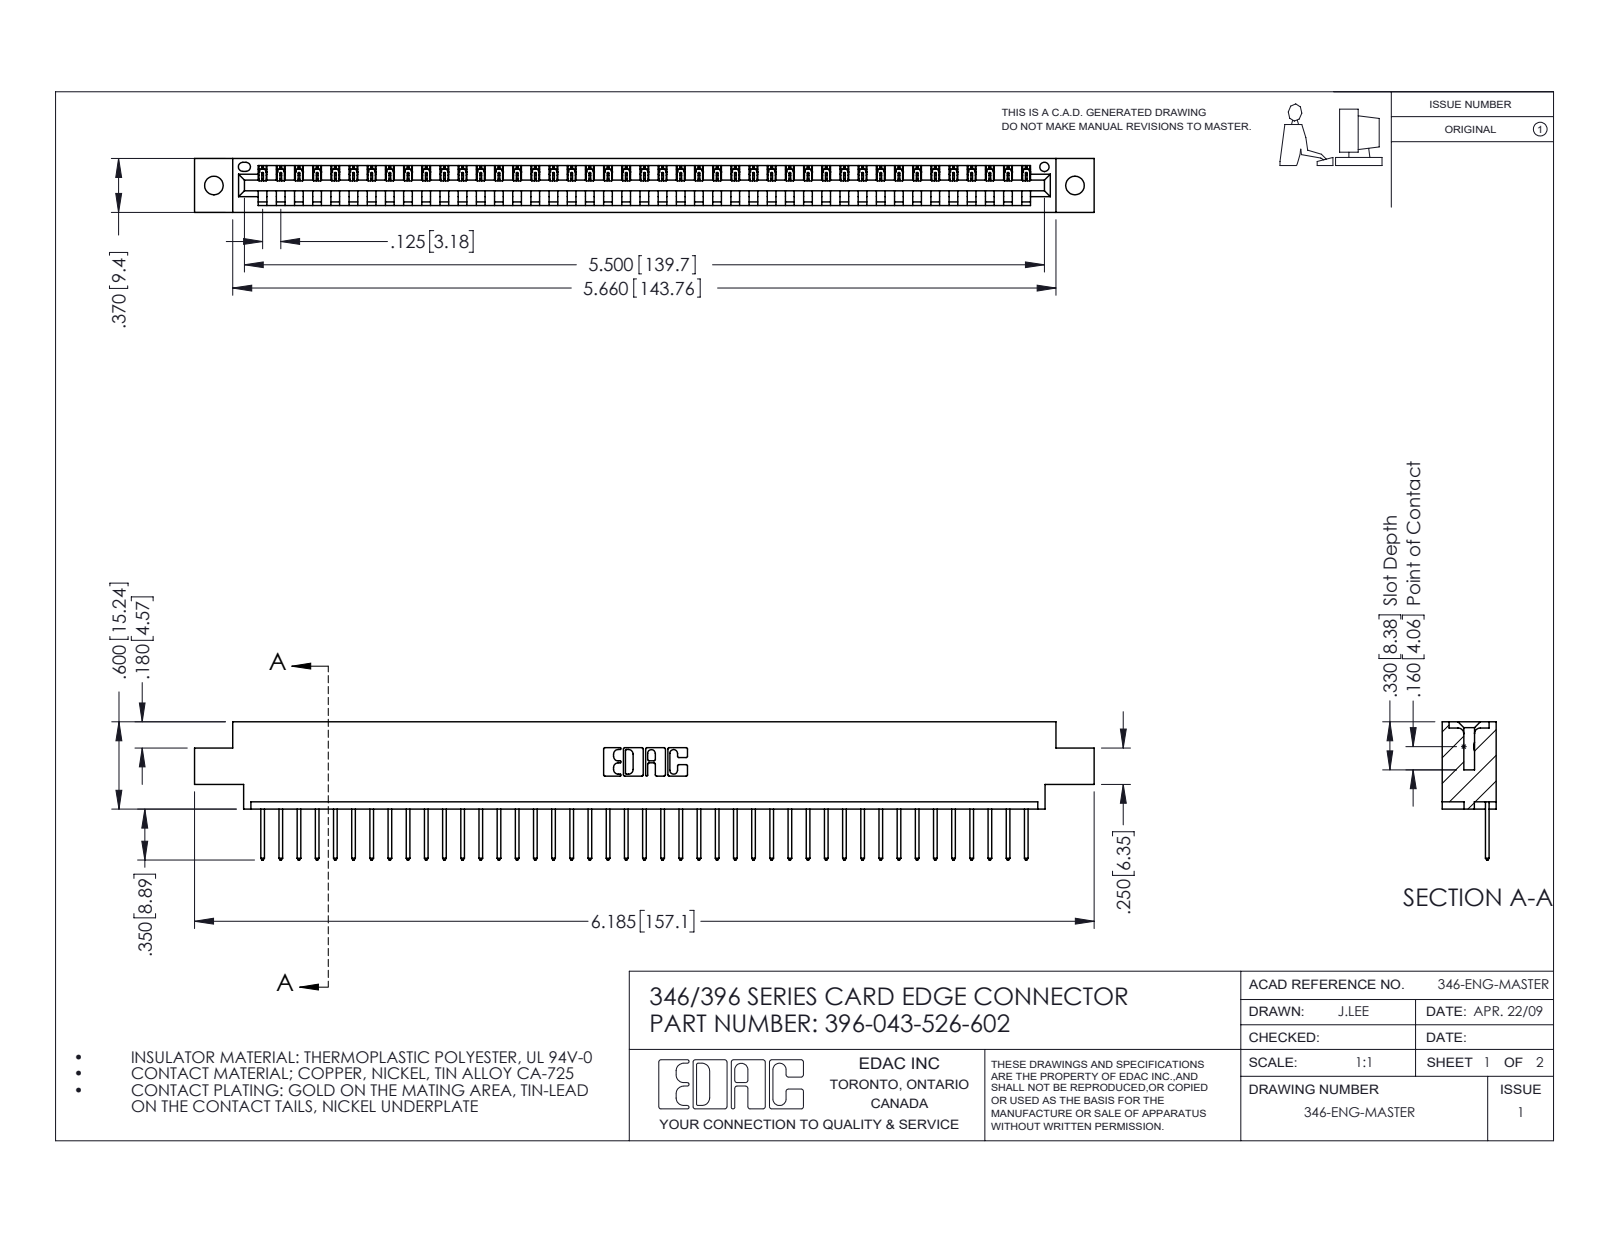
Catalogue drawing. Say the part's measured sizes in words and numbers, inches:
The part is named "346 Part_0.170 Offset - 0.128 Dia; 345-292-001_345-293-126; 396-043-526-602". Its 3-D file was written by "SolidWorks 2016 (CONFIG_CONTROL_DESIGN)". It is 44 solids with 2620 faces: 1800 planar, 820 cylindrical and 0 other. Overall it measures 6.185 by 0.95 by 0.37 inches. Its volume is 0.904 cubic inches and its surface area 28.49 square inches. Round holes: 2 of diameter 0.128, 1 of diameter 0.064. Partial cylindrical surfaces (rounded edges, fillets, slot ends): 86 of radius 0.006, 86 of radius 0.01, 22 of radius 0.01, 6 of radius 0.007, 6 of radius 0.031, 3 of radius 0.026, 2 of radius 0.031, 2 of radius 0.04. The main face-to-face distances are 0.048, 0.322, 0.37, 0.25, 0.072, 0.298, 0.025, 0.148, 0.222, 0.1. The hole center spacings are 0.246, 5.711, 5.92.
